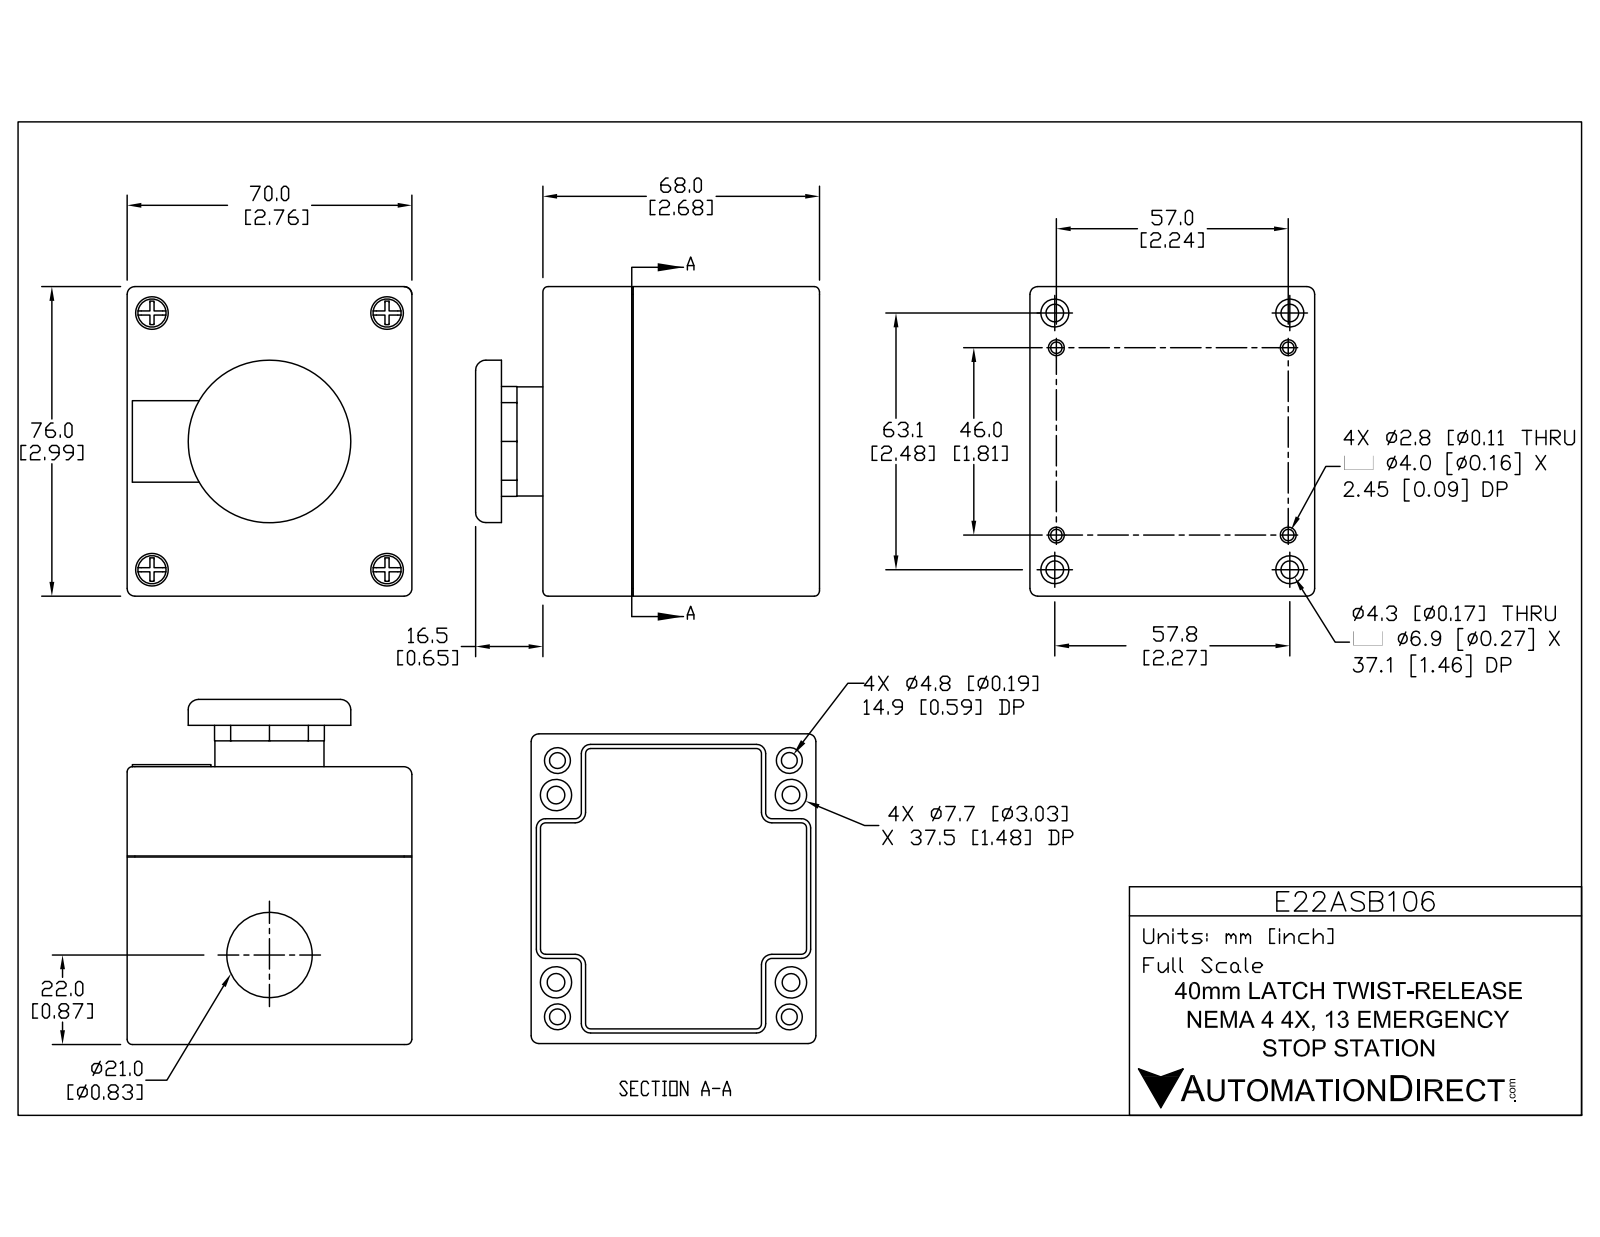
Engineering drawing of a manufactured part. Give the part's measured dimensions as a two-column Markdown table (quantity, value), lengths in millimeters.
| quantity | value |
| --- | --- |
| part name | E22ASB106 |
| STEP written by | SolidWorks 2017 (AUTOMOTIVE_DESIGN) |
| units | millimeters |
| bodies | 14 solids, 421 faces (305 planar, 98 cylindrical, 18 other) |
| overall size | 89.75 × 76 × 70 |
| volume | 180 782 mm³ |
| surface area | 74 181 mm² |
| round holes (diameter × count) | 8.5 × 4, 6 × 2, 17 × 1, 21 × 1, 21.5 × 1, 22 × 1, 22.2 × 1 |
| round bosses / shafts (diameter × count) | 6.5 × 4, 40 × 1, 29.5 × 1, 29 × 1, 28 × 1, 27 × 1, 24 × 1, 16 × 1 |
| partial cylindrical surfaces (radius × count) | 4 × 12, 3 × 10, 1 × 4, 2 × 4, 1.4 × 2, 12.25 × 1, 15 × 1 |
| main face-to-face distances | 3, 6, 70, 40, 19, 22, 68, 73, 46, 76 |
| hole center spacings | 42.48, 14.14, 28.36, 44.1, 45.44, 56.61, 57, 63 |
